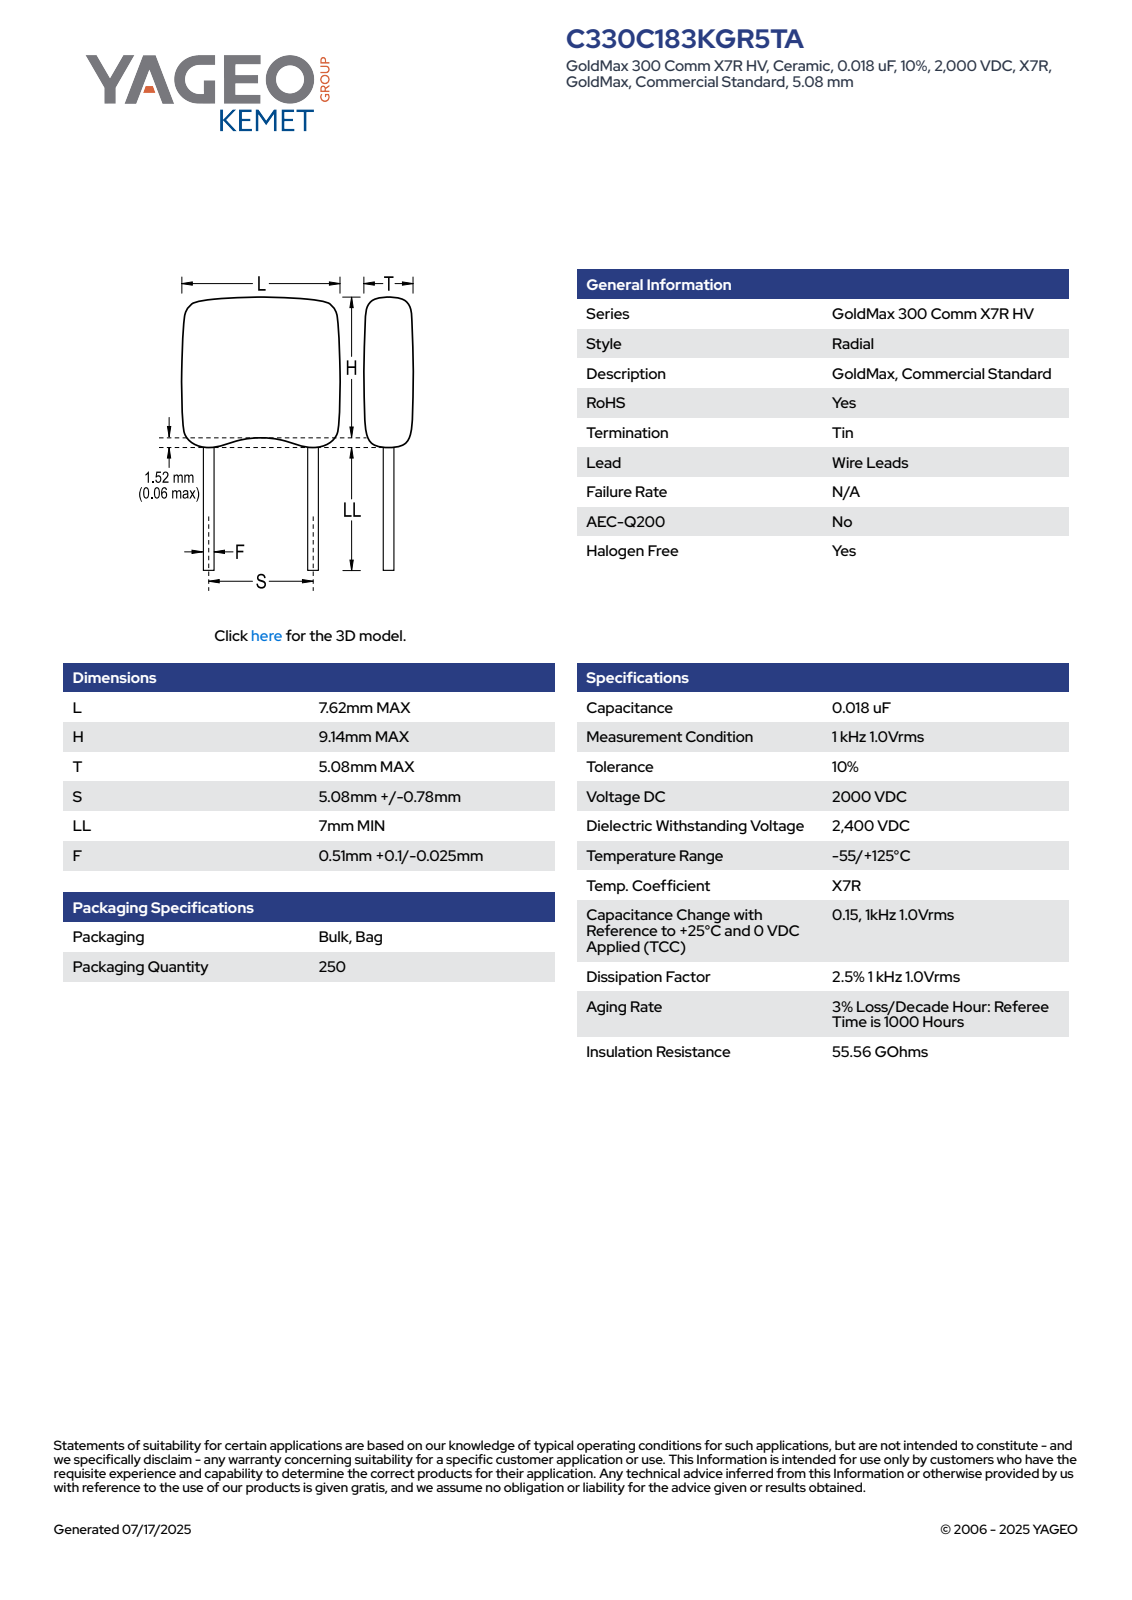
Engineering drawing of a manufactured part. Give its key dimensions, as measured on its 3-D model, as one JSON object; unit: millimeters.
{"part_name": "CCR_KRCST_C330_L7.62H9.14T5.08S5.08LL7F0.61", "step_written_by": "SolidWorks 2014 (AUTOMOTIVE_DESIGN)", "units": "millimeters", "bodies": {"solids": 4, "faces": 83, "planar": 65, "cylindrical": 14, "other": 4}, "overall_size": [17.66, 7.62, 5.08], "volume_mm3": 407, "surface_area_mm2": 352, "round_bosses_or_shafts": [[0.61, 2]], "partial_cylinders_radius": [[0.75, 10]], "face_to_face_distances": [5.08, 7.62, 10.66, 7, 17.66, 12.8, 5.8, 4.86, 11.99, 4.99]}
